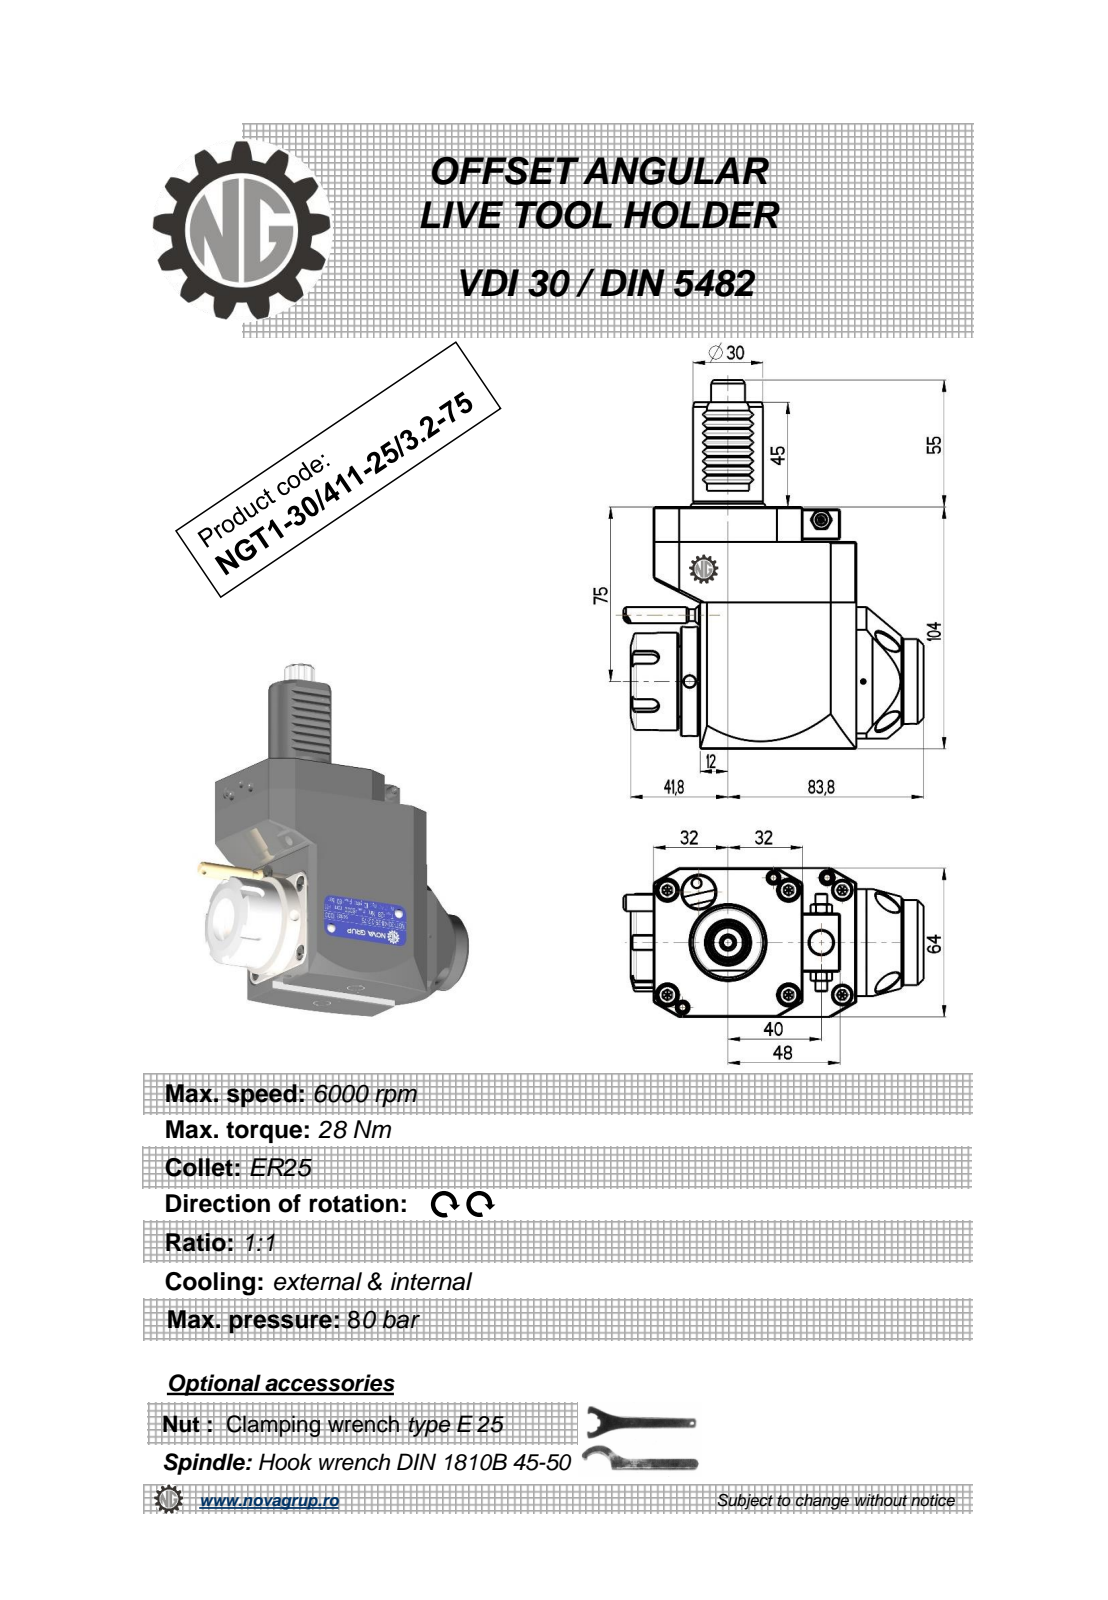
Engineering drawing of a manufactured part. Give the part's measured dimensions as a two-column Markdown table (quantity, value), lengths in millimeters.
| quantity | value |
| --- | --- |
| part name | NGT1_30_411_25_3_2_75 |
| STEP written by | PRO/ENGINEER BY PARAMETRIC TECHNOLOGY CORPORATION, 2010280 (CONFIG_CONTROL_DESIGN) |
| units | millimeters |
| bodies | 1 solid, 451 faces (183 planar, 110 cylindrical, 158 other) |
| overall size | 159 × 128.63 × 64 |
| volume | 580 728 mm³ |
| surface area | 55 267 mm² |
| round holes (diameter × count) | 5 × 2, 2.5 × 1, 3 × 1, 4.2 × 1, 9.5 × 1, 10 × 1, 20.3 × 1 |
| round bosses / shafts (diameter × count) | 5 × 2, 47 × 1, 42 × 1, 36.5 × 1, 35 × 1, 30 × 1, 8.96 × 1, 7 × 1 |
| partial cylindrical surfaces (radius × count) | 2.81 × 16, 0.26 × 12, 0.3 × 8, 3 × 5, 160 × 2, 5.67 × 1, 7.25 × 1, 32 × 1 |
| main face-to-face distances | 64, 104, 87, 15, 89, 20, 19.8, 0.5, 67.2, 67 |
| hole center spacings | 33.19, 43, 56.45, 68, 89.54 |
